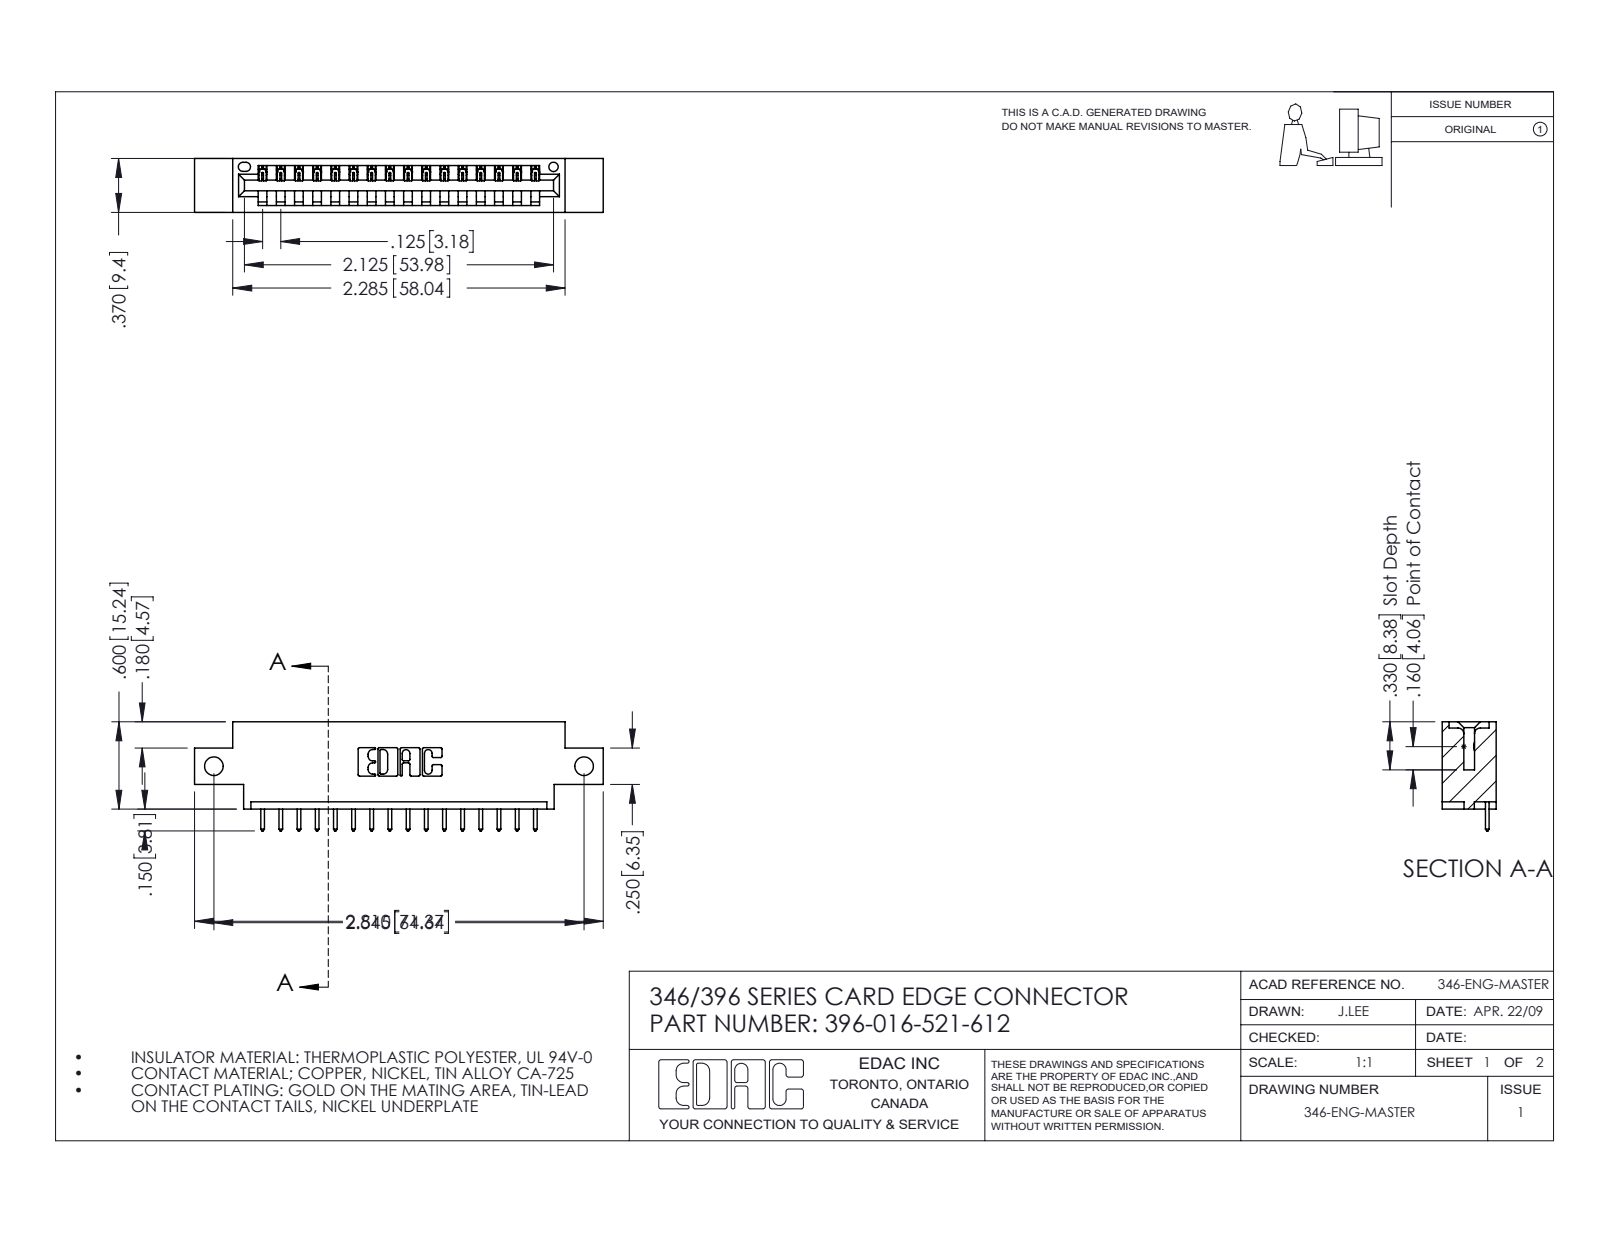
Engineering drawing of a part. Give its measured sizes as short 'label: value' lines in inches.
name: 345-292-001_345-293-121; 396-016-521-612; 346 Part_0.170 Offset - Side Mount
written by: SolidWorks 2016 (CONFIG_CONTROL_DESIGN)
unit: in
bodies: 17 solids, 1054 faces (720 planar, 334 cylindrical, 0 other)
size: 2.81 × 0.75 × 0.37
volume: 0.388 in³; area: 11.64 in²
holes: 2× ⌀0.128, 1× ⌀0.064
rounds: 32× R0.006, 32× R0.01, 22× R0.01, 6× R0.007, 6× R0.031, 3× R0.026, 2× R0.031, 2× R0.04
face distances: 0.37, 0.048, 0.322, 0.25, 0.072, 0.298, 0.025, 0.148, 0.222, 0.1
hole spacings: 2.545
